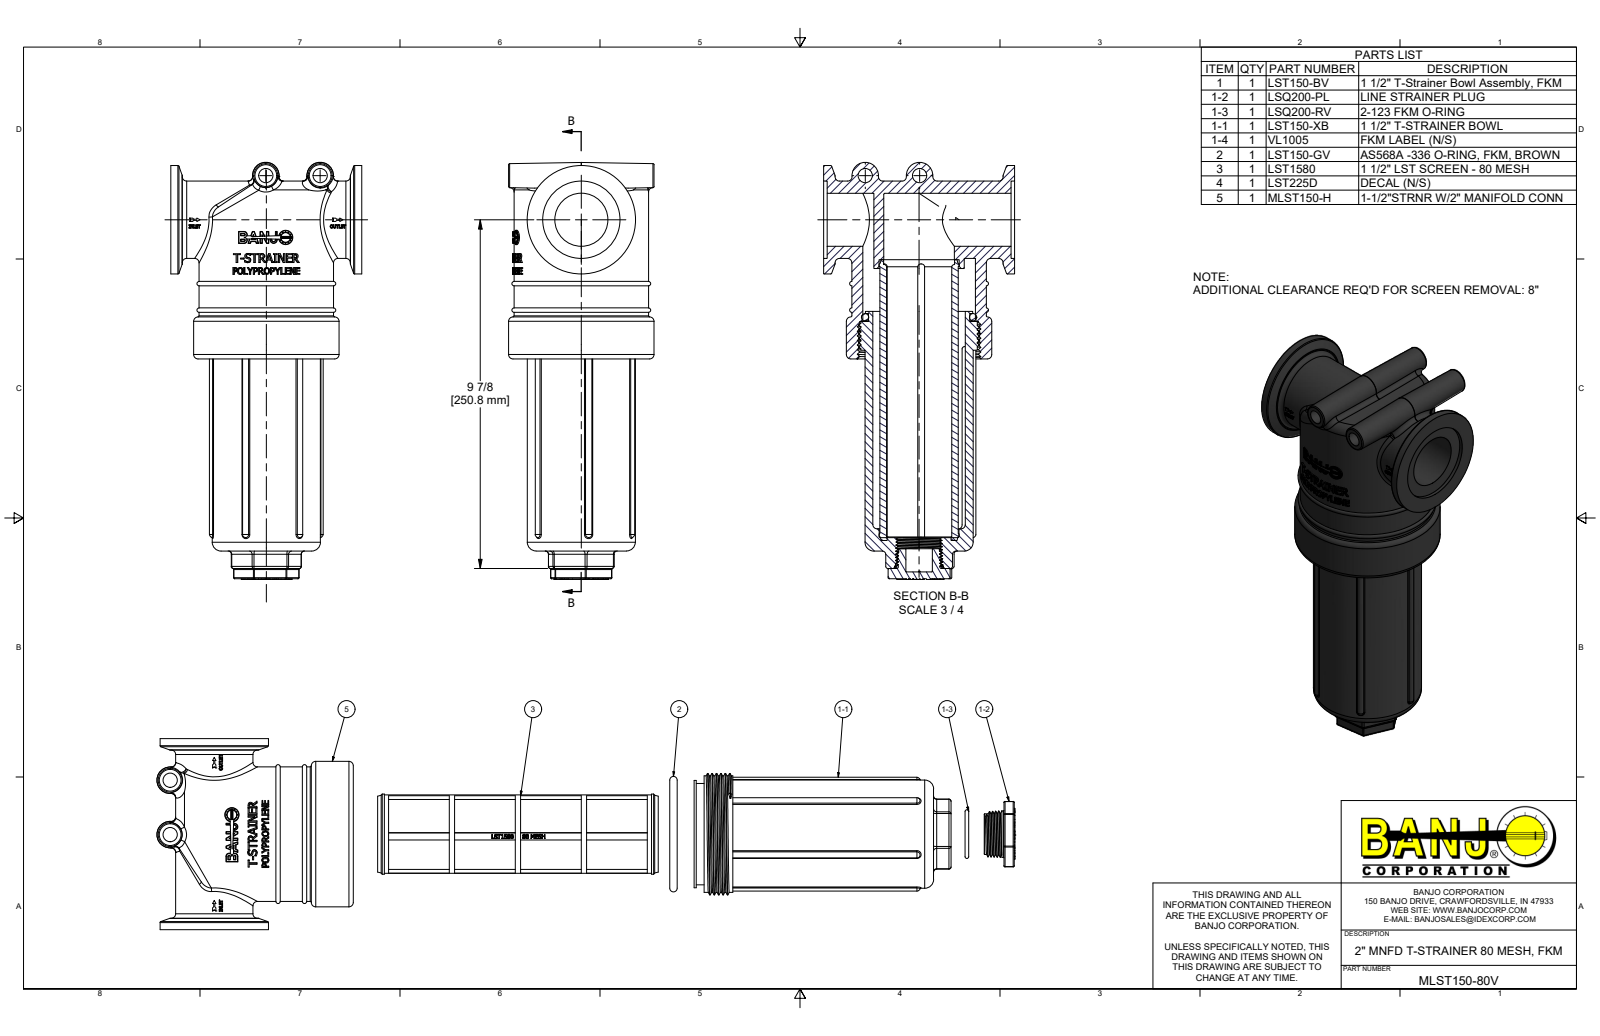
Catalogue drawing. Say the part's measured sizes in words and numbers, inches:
The part is named "MLST150-80V; MLST150-H; LST150-BV; LST150-XB (+5 more)". Its 3-D file was written by "Autodesk Inventor 2019 (AUTOMOTIVE_DESIGN)". It is 7 solids with 2267 faces: 1226 planar, 290 cylindrical and 751 other. Overall it measures 11.81 by 5.41 by 4.12 inches. Its volume is 52.34 cubic inches and its surface area 502.3 square inches. Round holes: 2 of diameter 0.406, 1 of diameter 0.272, 1 of diameter 0.385, 1 of diameter 0.75, 1 of diameter 1.5, 1 of diameter 1.81, 1 of diameter 1.97, 1 of diameter 2, 1 of diameter 2.26, 1 of diameter 2.62, 1 of diameter 3.19, 1 of diameter 3.365. Round bosses or shafts: 1 of diameter 4.12, 1 of diameter 3.81, 1 of diameter 3.435, 1 of diameter 3.3, 1 of diameter 3.07, 1 of diameter 3.063, 1 of diameter 3.04, 1 of diameter 2.87. Partial cylindrical surfaces (rounded edges, fillets, slot ends): 46 of radius 0.03, 13 of radius 0.06, 6 of radius 0.078, 6 of radius 0.09, 6 of radius 0.094, 5 of radius 0.1, 2 of radius 0.024, 2 of radius 0.034. The main face-to-face distances are 0.1, 5.31, 5.41, 3.63, 6.12, 9.75, 5.06, 1.06, 4.69, 1.24. The hole center spacings are 1.54, 1.838, 2.004.
